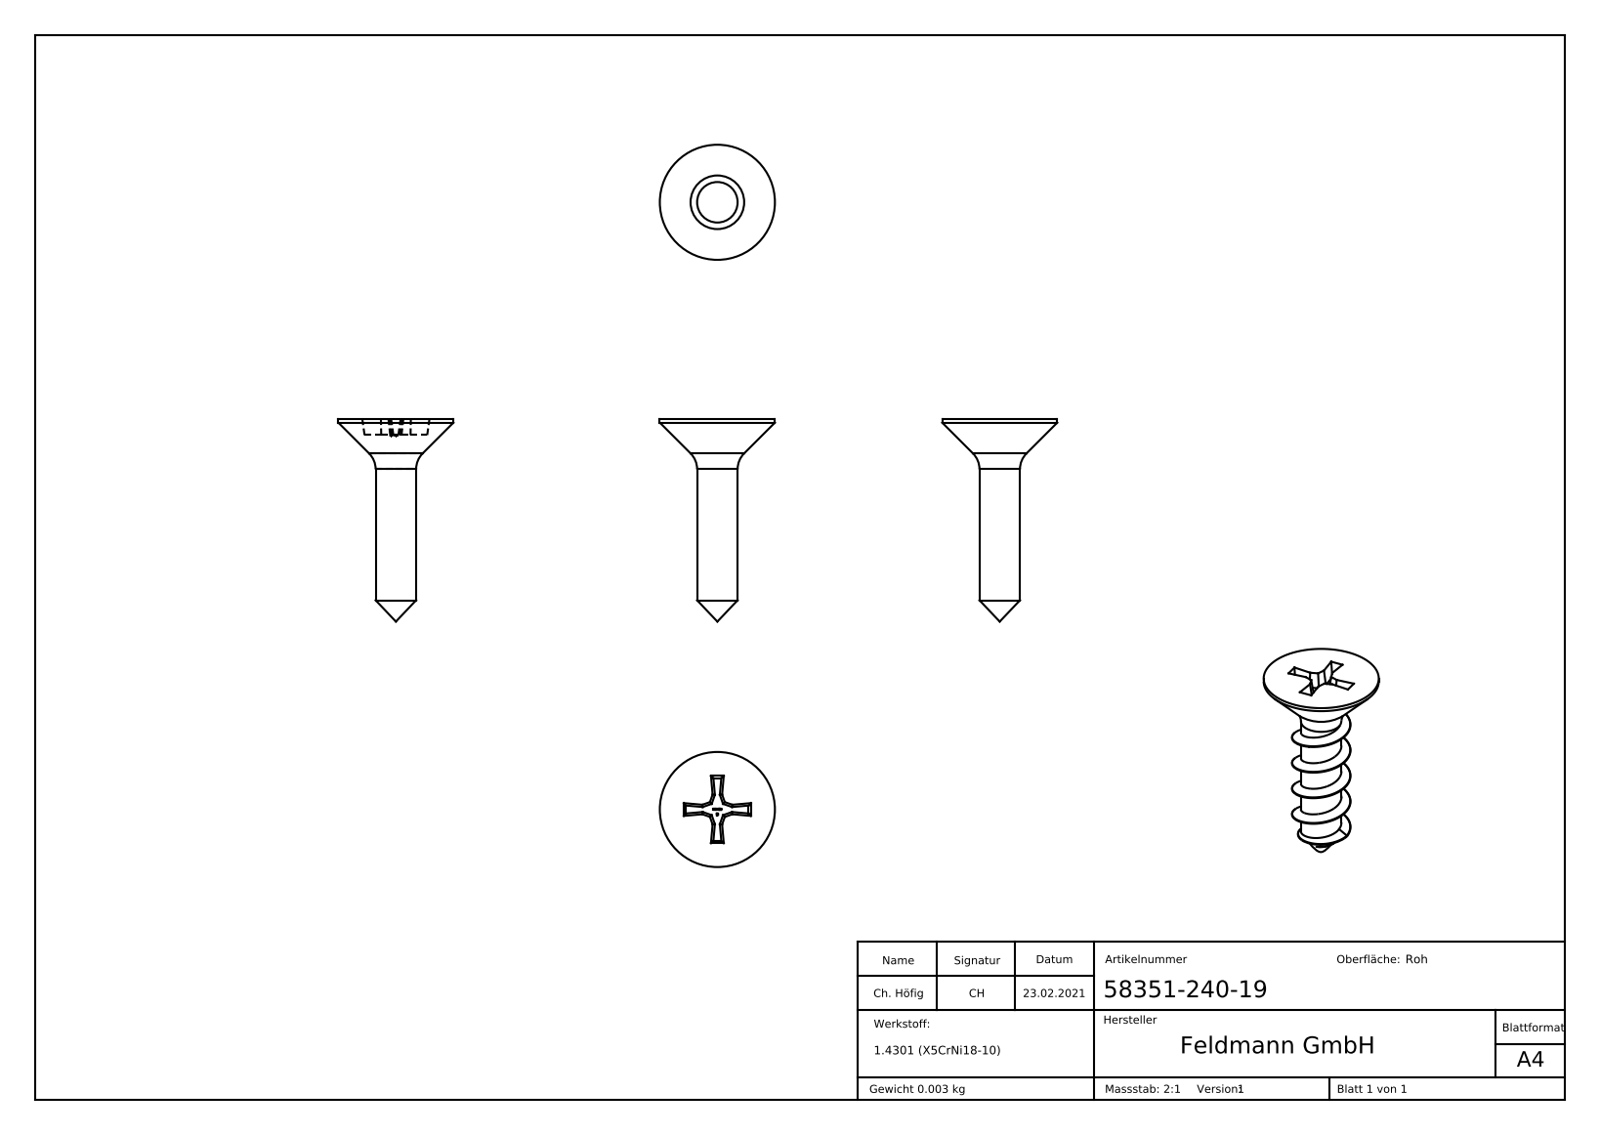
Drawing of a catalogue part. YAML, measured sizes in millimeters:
part_name: "58351-240-19"
step_written_by: "SolidWorks 2018 (CONFIG_CONTROL_DESIGN)"
units: millimeters
bodies: {solids: 1, faces: 331, planar: 182, cylindrical: 4, other: 145}
overall_size: [19, 10.8, 10.8]
volume: 331
surface_area: 421
round_bosses_or_shafts:
  - {diameter: 10.8, count: 1}
  - {diameter: 3.8, count: 1}
face_to_face_distances: [1.5, 0.38, 0.4, 0.39, 0.36, 0.41, 0.37, 1.6, 0.42, 0.43]
